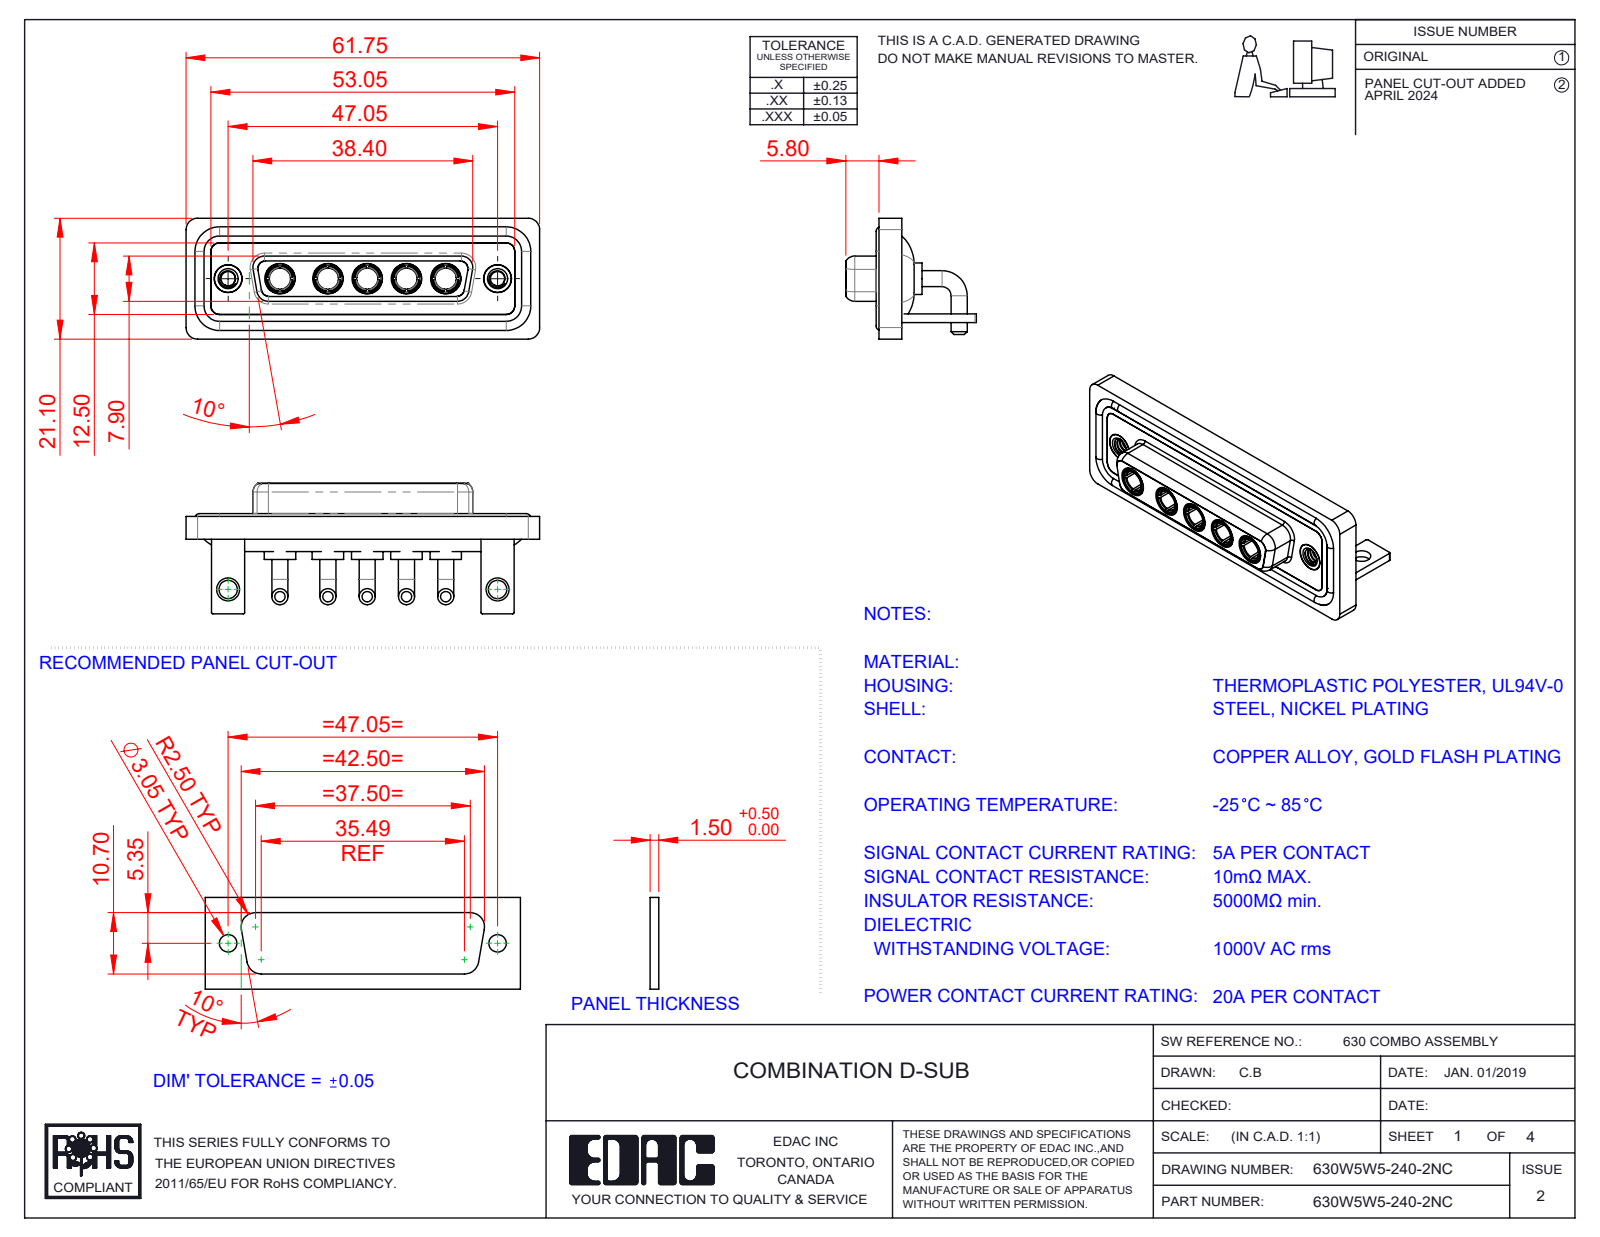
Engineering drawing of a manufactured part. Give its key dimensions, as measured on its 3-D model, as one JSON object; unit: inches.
{"part_name": "630Combo Shell Rear_25 Contacts; Power Socket_20A RA; 630Combo Shell Front_25 Contacts; 630W5W5-140-2NC (+4 more)", "step_written_by": "SolidWorks 2023 (CONFIG_CONTROL_DESIGN)", "units": "inches", "bodies": {"solids": 19, "faces": 818, "planar": 270, "cylindrical": 335, "other": 213}, "overall_size": [2.431, 0.898, 0.831], "volume_in3": 0.537, "surface_area_in2": 22.56, "round_holes": [[0.191, 7], [0.146, 5], [0.209, 5], [0.098, 2], [0.126, 2], [0.157, 2], [0.159, 2], [0.197, 2]], "round_bosses_or_shafts": [[0.11, 10], [0.217, 5], [0.205, 5], [0.195, 5], [0.187, 5], [0.148, 5], [0.063, 4], [0.195, 2]], "partial_cylinders_radius": [[0.079, 19], [0.059, 18], [0.01, 16], [0.053, 8], [0.063, 8], [0.02, 5], [0.083, 5], [0.024, 4]], "face_to_face_distances": [0.016, 0.071, 0.114, 0.146, 0.059, 0.161, 0.043, 0.055, 0.063, 0.098], "hole_center_spacings": [0.27, 0.356, 1.496, 1.852, 0.27, 0.33, 0.54, 0.541]}
